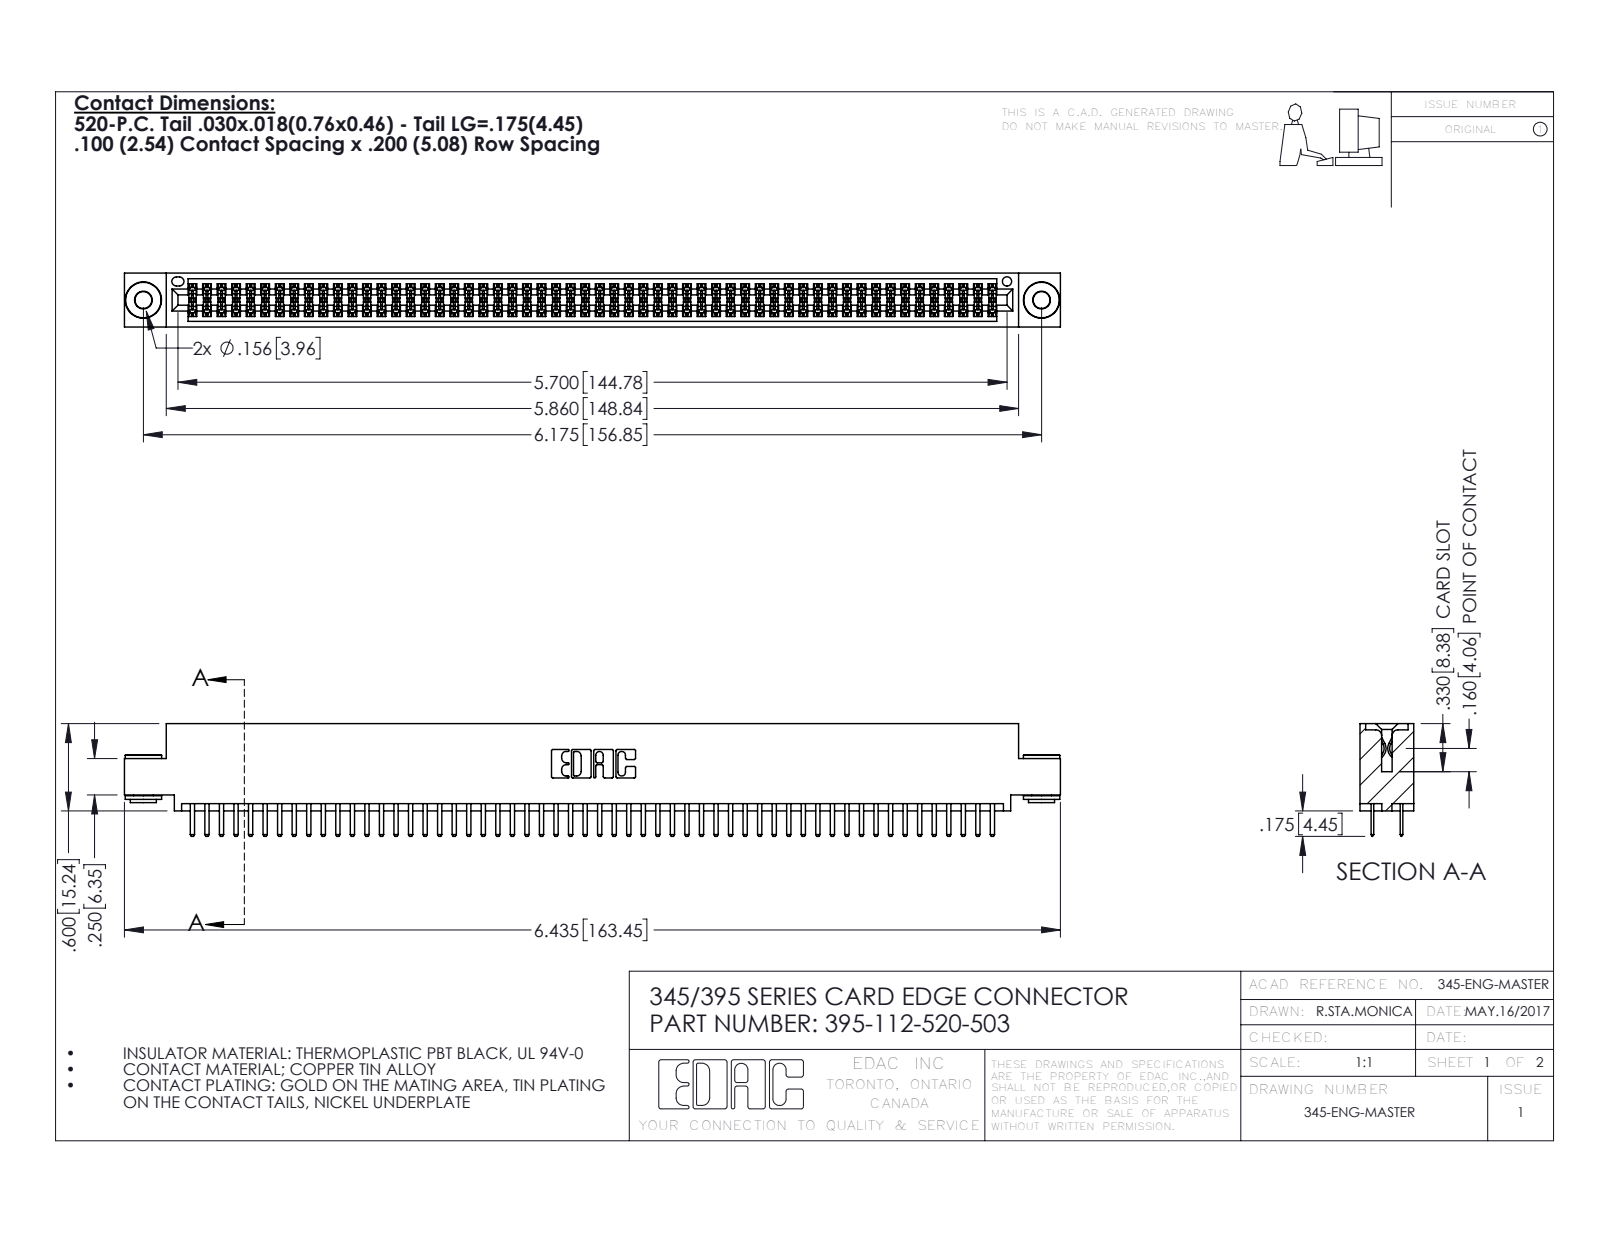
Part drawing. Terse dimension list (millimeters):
name: 395-112-520-503; 345 Part_0.110 Offset - 0.156 Dia-TH; 345-292-001_345-293-120; 345-250-002_345-250-002-102
written by: SolidWorks 2016 (CONFIG_CONTROL_DESIGN)
unit: mm
bodies: 115 solids, 6216 faces (4014 planar, 2194 cylindrical, 8 other)
size: 163.4 × 19.7 × 9.4
volume: 15 900 mm³; area: 23 970 mm²
holes: 2× ⌀2.9, 2× ⌀4, 1× ⌀1.6
bosses: 2× ⌀6.4, 2× ⌀4.6, 2× ⌀3.5
rounds: 168× R0.2, 116× R0.3, 22× R0.3, 6× R0.2, 6× R0.8, 3× R0.7, 2× R0.4, 2× R0.5
face distances: 1.8, 7.6, 5.1, 9.4, 0.6, 2.5, 6.9, 5.7, 0.6, 1.8
hole spacings: 6.9, 150.9, 156.8
